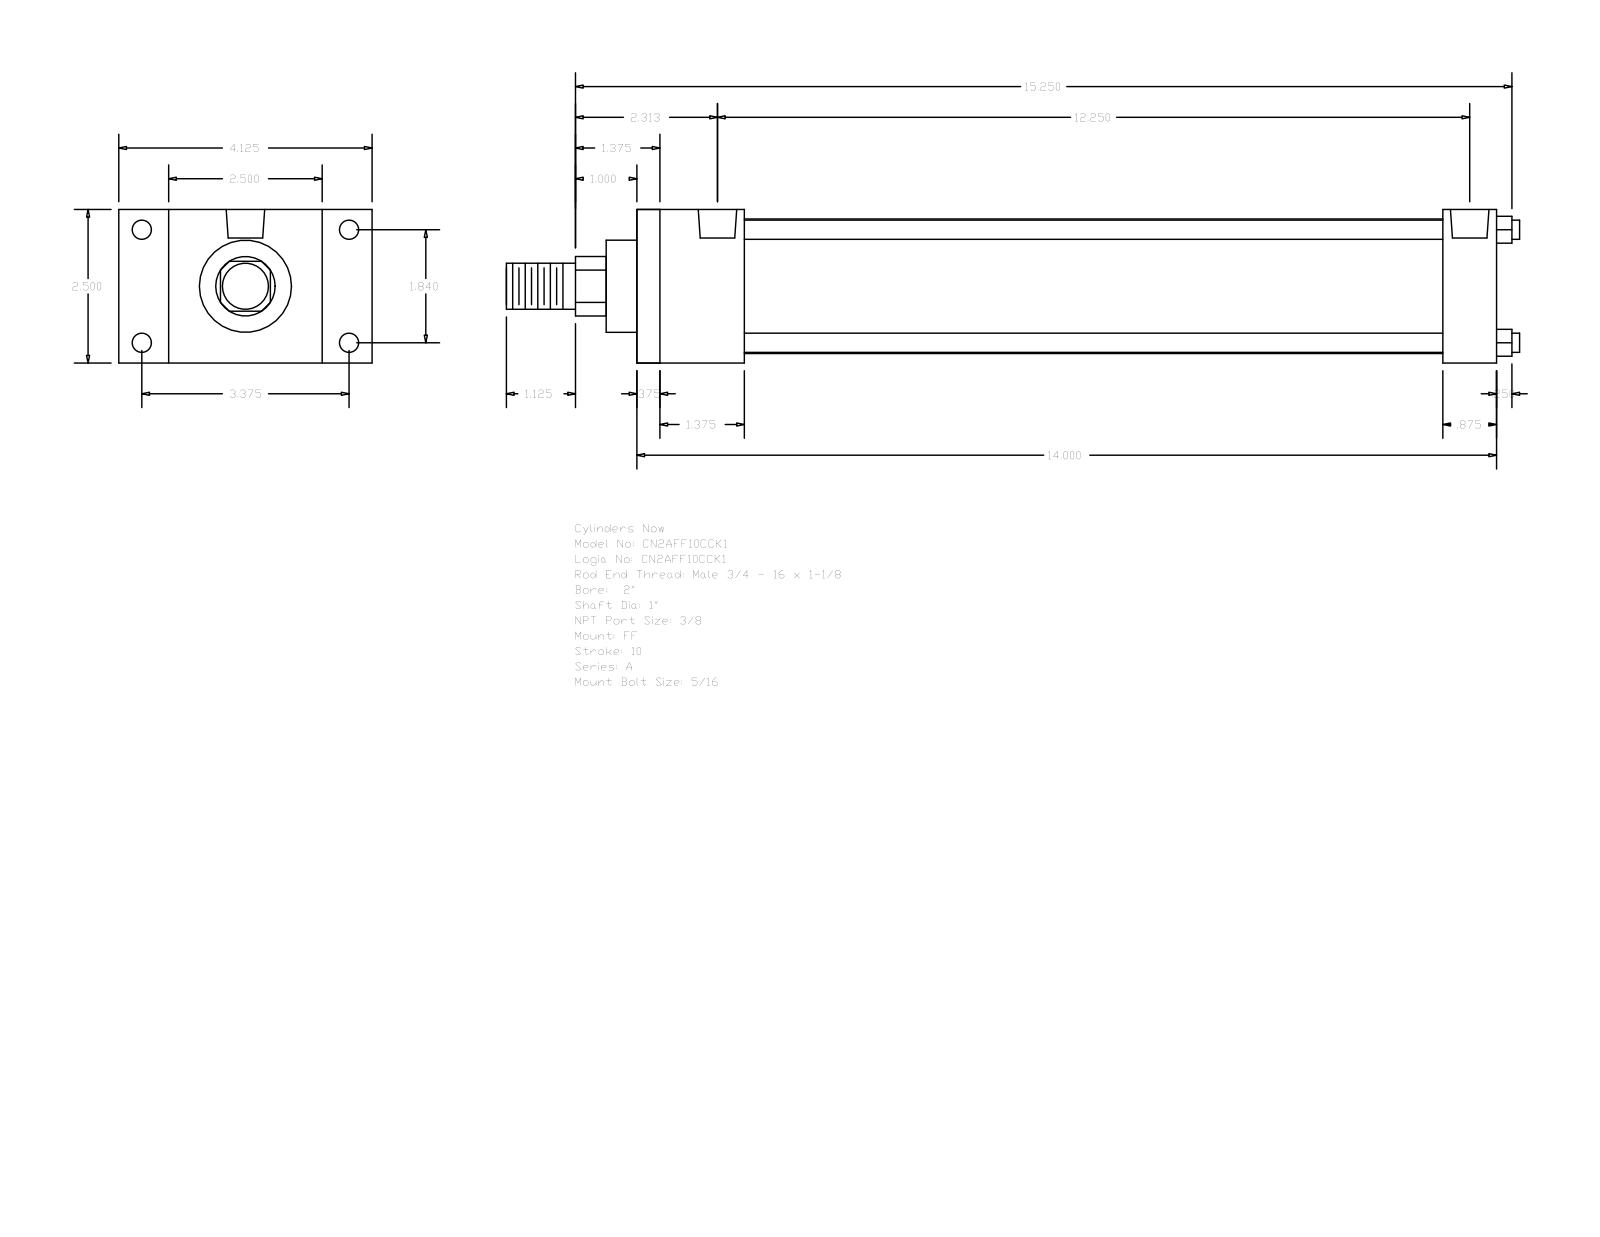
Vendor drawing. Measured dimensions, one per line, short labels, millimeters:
name: A_FF__0200_1
written by: GSSL Pune (CONFIG_CONTROL_DESIGN)
unit: mm
bodies: 0 solids, 92 faces (64 planar, 28 cylindrical, 0 other)
size: 419.1 × 104.78 × 63.5
holes: 4× ⌀5.56, 4× ⌀7.94, 2× ⌀15.93
bosses: 4× ⌀7.94, 1× ⌀55.63, 1× ⌀38.1, 1× ⌀25.4, 1× ⌀19.05
rounds: 1× R12.29
face distances: 63.5, 355.6, 9.52, 346.08, 20.64, 44.45, 333.37, 34.93, 323.85, 288.92
hole spacings: 46.74, 85.72, 97.63, 305.58, 1.59, 3.98, 307.17, 309.56
